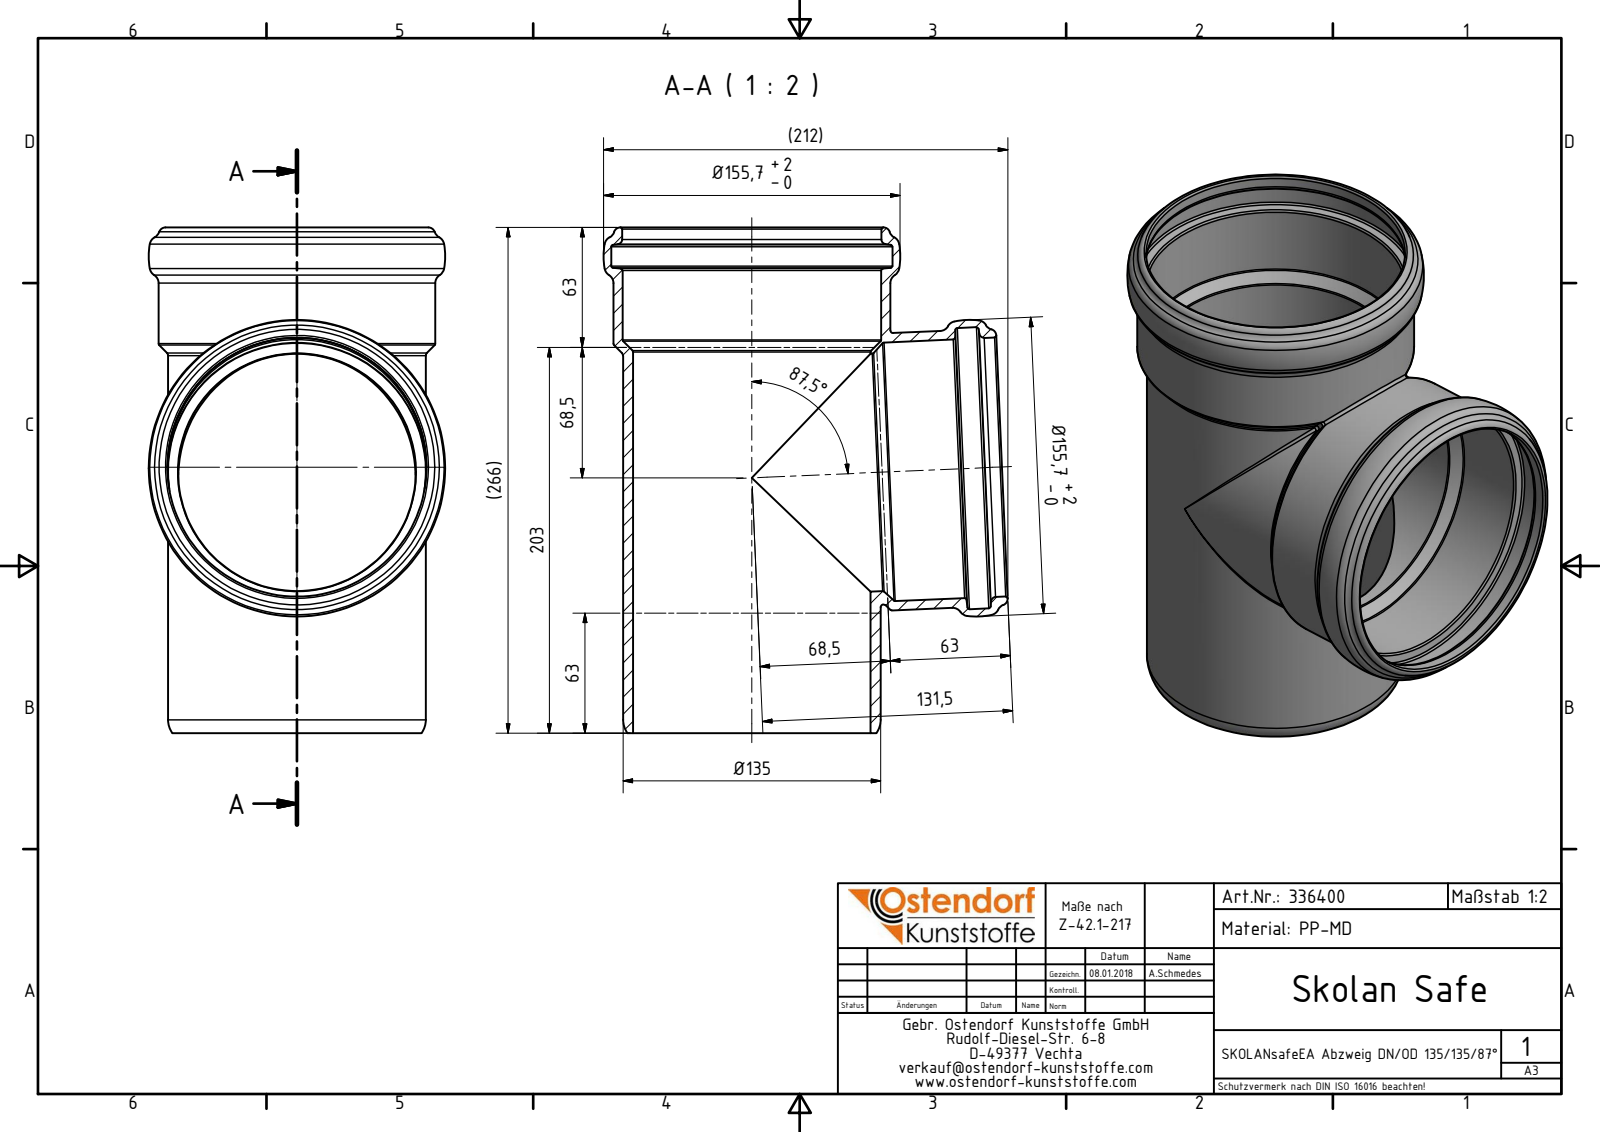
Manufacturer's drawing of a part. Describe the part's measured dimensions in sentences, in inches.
The part is named "336400 SKOLANsafeEA Abzweiger DN_OD 135_135_87°". Its 3-D file was written by "Autodesk Inventor 2016 (AUTOMOTIVE_DESIGN)". It is 1 solid with 69 faces: 1 planar, 14 cylindrical and 54 other. Overall it measures 10.453 by 8.356 by 6.13 inches. Its volume is 42.47 cubic inches and its surface area 440.7 square inches. Round holes: 2 of diameter 4.909, 2 of diameter 5.346, 2 of diameter 5.358, 2 of diameter 5.815. Round bosses or shafts: 2 of diameter 5.724, 1 of diameter 5.327. Partial cylindrical surfaces (rounded edges, fillets, slot ends): 1 of radius 2.663.
